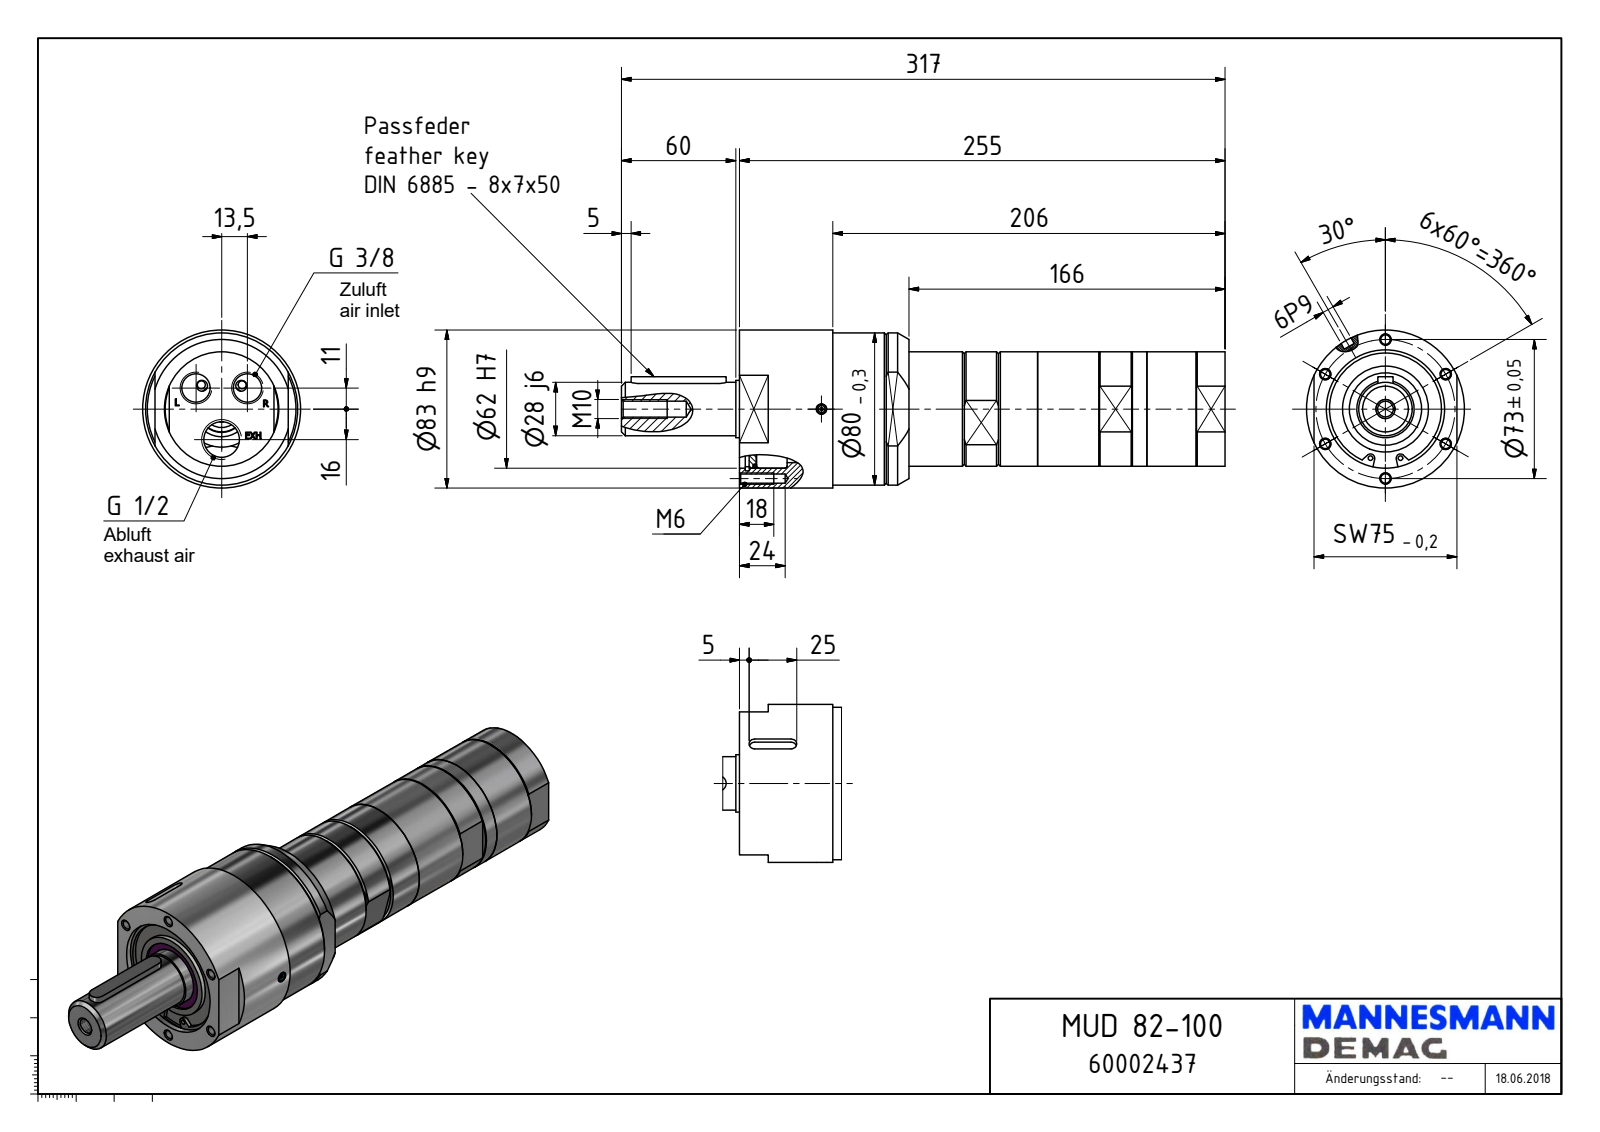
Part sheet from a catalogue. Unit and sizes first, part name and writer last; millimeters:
Units: millimetres
Overall size (bounding box): 317 × 83 × 83
Round holes (diameter × count): ⌀4.92 ×6, ⌀1.55 ×3, ⌀4 ×2, ⌀5.5 ×2, ⌀14.95 ×2, ⌀8.38 ×1, ⌀18.63 ×1, ⌀36.5 ×1, ⌀38 ×1, ⌀40 ×1, ⌀62 ×1, ⌀65 ×1
Round bosses / shafts (diameter × count): ⌀5 ×2, ⌀3.6 ×2, ⌀83 ×1, ⌀80 ×1, ⌀67.11 ×1, ⌀60 ×1, ⌀45 ×1, ⌀30 ×1
Partial cylindrical surfaces — rounded edges, fillets, slot ends (radius × count): R3 ×2, R4 ×2, R7.5 ×2, R8.5 ×1, R19.35 ×1, R23.5 ×1, R25.34 ×1, R32.5 ×1
Main face-to-face distances: 255, 2.5, 5, 250, 65, 89, 84, 166, 10, 55
Hole centre spacings: 36.5, 63.22, 73, 17.41, 19.51, 28.85, 30.19, 31.69
Volume: 933 140 mm³ · Surface area: 83 142 mm²
Bodies: 1 solid, 259 faces (127 planar, 67 cylindrical, 65 other)
Part name (STEP PRODUCT): MUD 82-100_60002437
STEP written by: Autodesk Inventor 2018 (AUTOMOTIVE_DESIGN)
